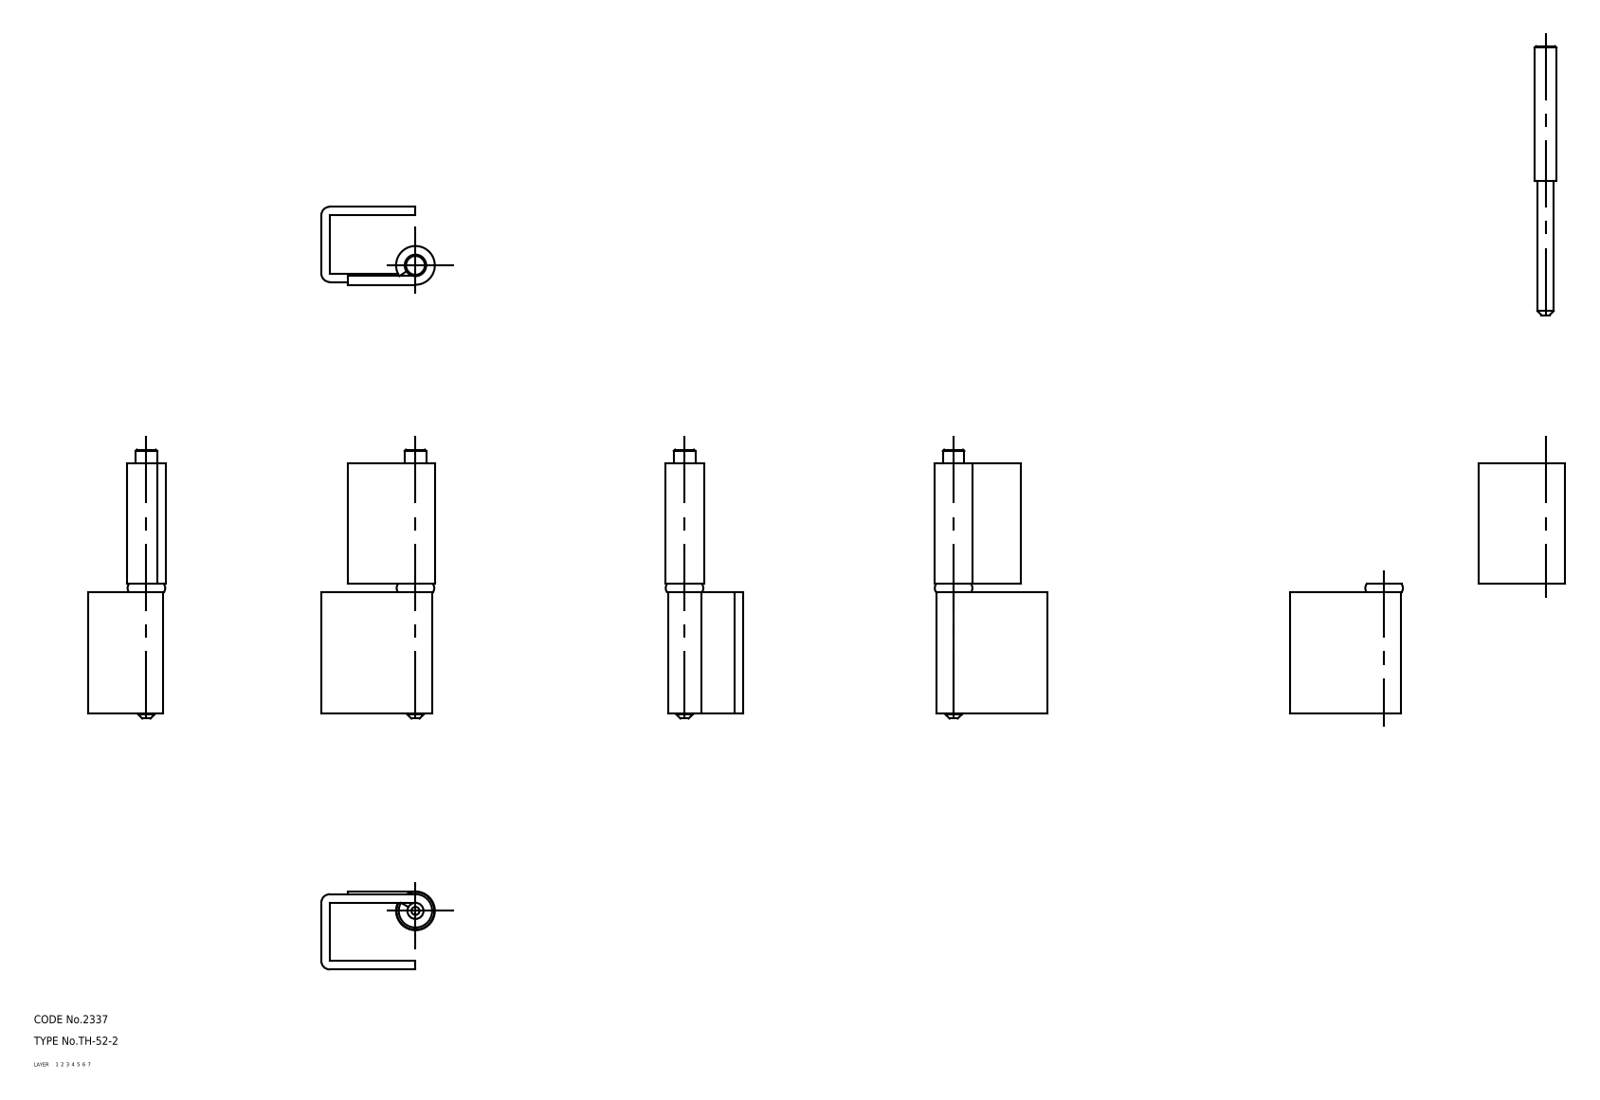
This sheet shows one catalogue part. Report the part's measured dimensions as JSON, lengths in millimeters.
{"part_name": "washer; shaft; hinge piece_B; hinge piece_A (+1 more)", "step_written_by": "CADfix (AUTOMOTIVE_DESIGN)", "units": "millimeters", "bodies": {"solids": 4, "faces": 39, "planar": 0, "cylindrical": 0, "other": 39}, "overall_size": [100, 42.2, 29], "volume_mm3": 28582, "surface_area_mm2": 19527}
